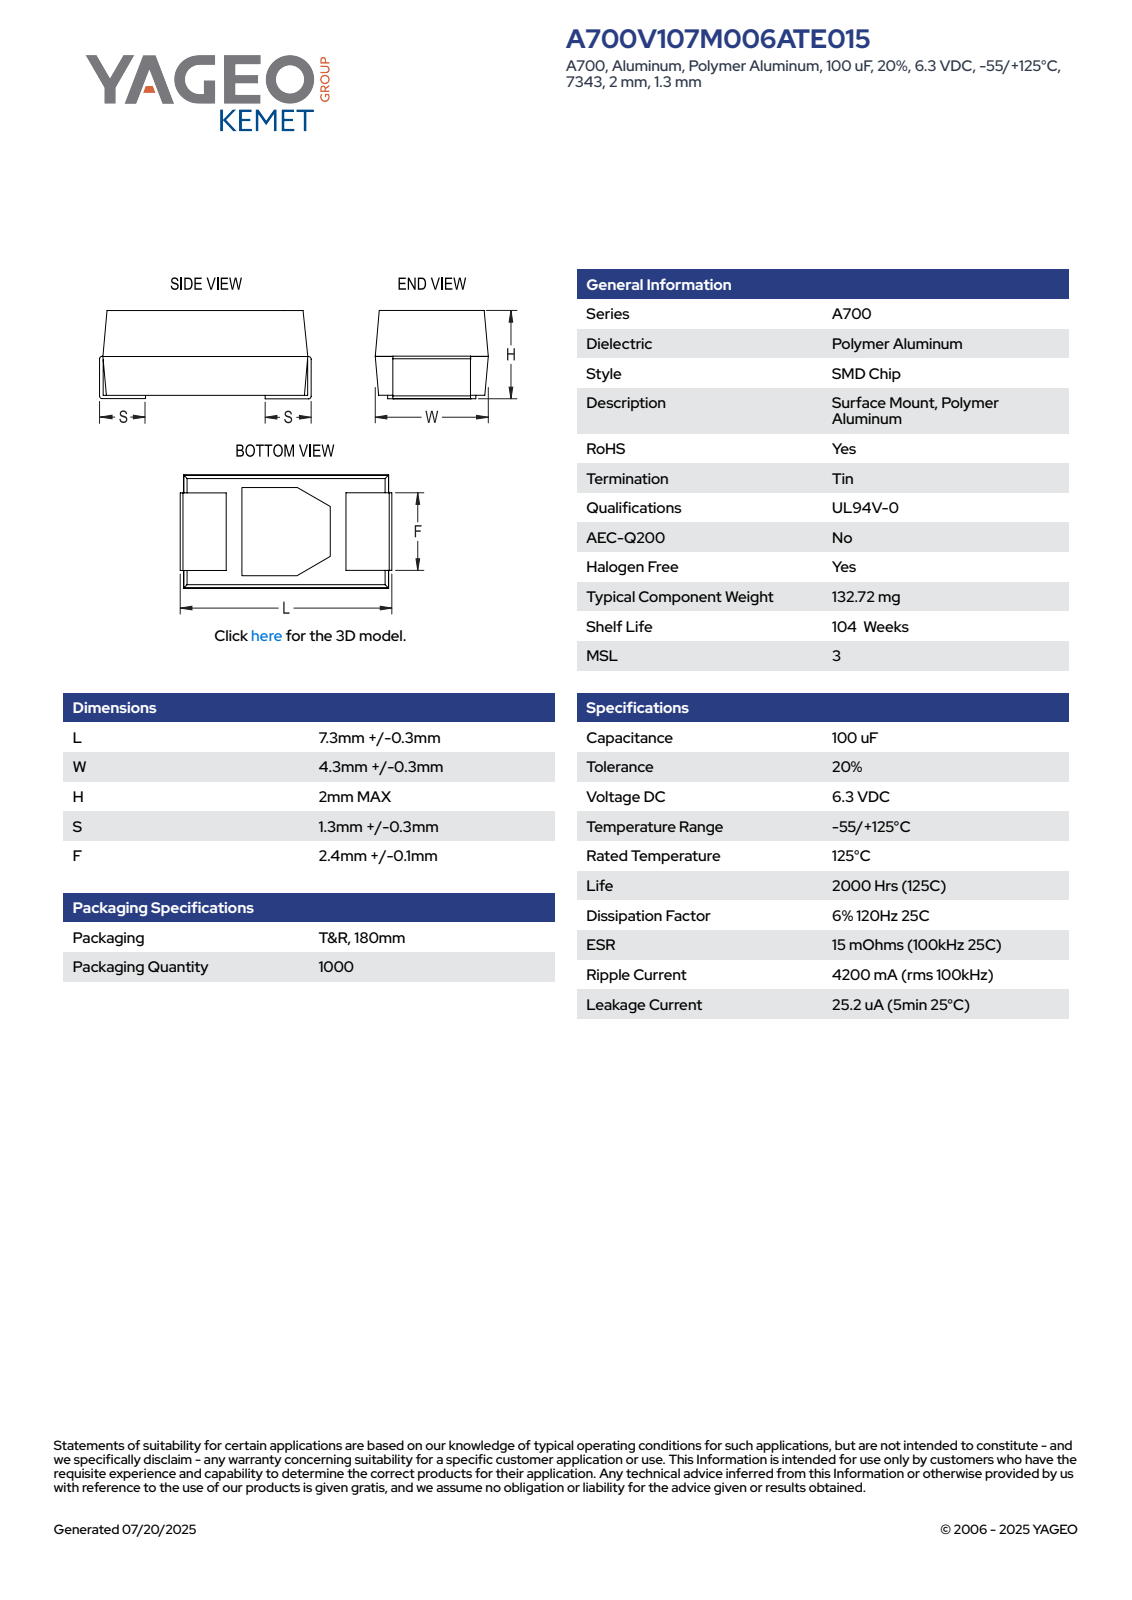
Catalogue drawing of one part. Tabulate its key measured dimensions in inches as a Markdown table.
| quantity | value |
| --- | --- |
| part name | CAS_SMD_L7.6W4.6H2S1.3F2.5 |
| STEP written by | SolidWorks 2021 (AUTOMOTIVE_DESIGN) |
| units | inches |
| bodies | 1 solid, 82 faces (78 planar, 4 cylindrical, 0 other) |
| overall size | 0.299 × 0.181 × 0.079 |
| volume | 0.004 in³ |
| surface area | 0.186 in² |
| partial cylindrical surfaces (radius × count) | 0.004 × 4 |
| main face-to-face distances | 0.075, 0.079, 0.177, 0.178, 0.295, 0.281, 0.282, 0.291, 0.299, 0.079 |
